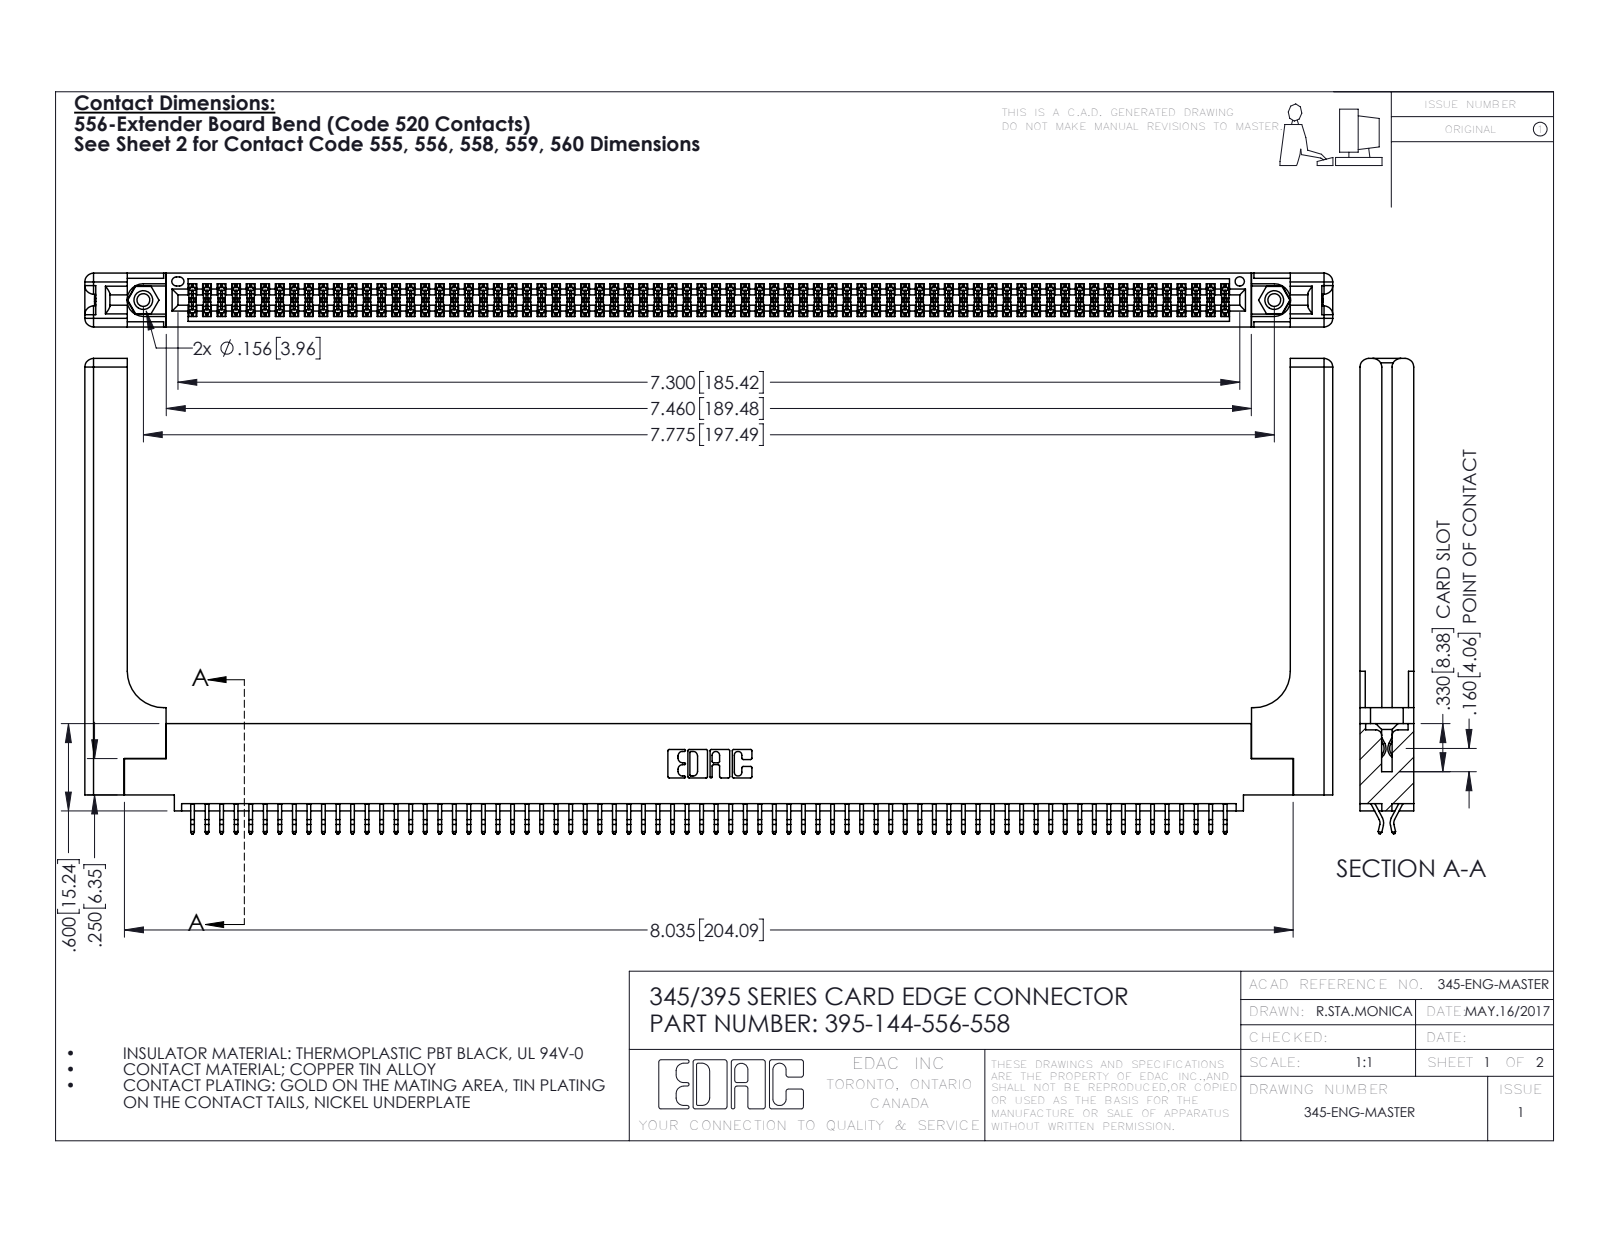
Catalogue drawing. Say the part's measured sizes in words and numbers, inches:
The part is named "345-292-001_556 Tail; 345-250-001_345-250-001-102; 395-144-556-558; 345 Part_0.110 Offset - 0.156 Dia-TH (+1 more)". Its 3-D file was written by "SolidWorks 2016 (CONFIG_CONTROL_DESIGN)". It is 149 solids with 8450 faces: 5560 planar, 2830 cylindrical and 60 other. Overall it measures 8.579 by 3.267 by 0.37 inches. Its volume is 1.821 cubic inches and its surface area 57.65 square inches. Round holes: 2 of diameter 0.089, 2 of diameter 0.125, 2 of diameter 0.156, 1 of diameter 0.064. Round bosses or shafts: 2 of diameter 0.155. Partial cylindrical surfaces (rounded edges, fillets, slot ends): 216 of radius 0.006, 22 of radius 0.01, 16 of radius 0.06, 6 of radius 0.007, 6 of radius 0.031, 3 of radius 0.026, 2 of radius 0.01, 2 of radius 0.014. The main face-to-face distances are 0.072, 0.298, 0.37, 0.025, 0.098, 0.272, 0.2, 0.225, 0.175, 0.148. The hole center spacings are 0.27, 7.539, 7.775.
